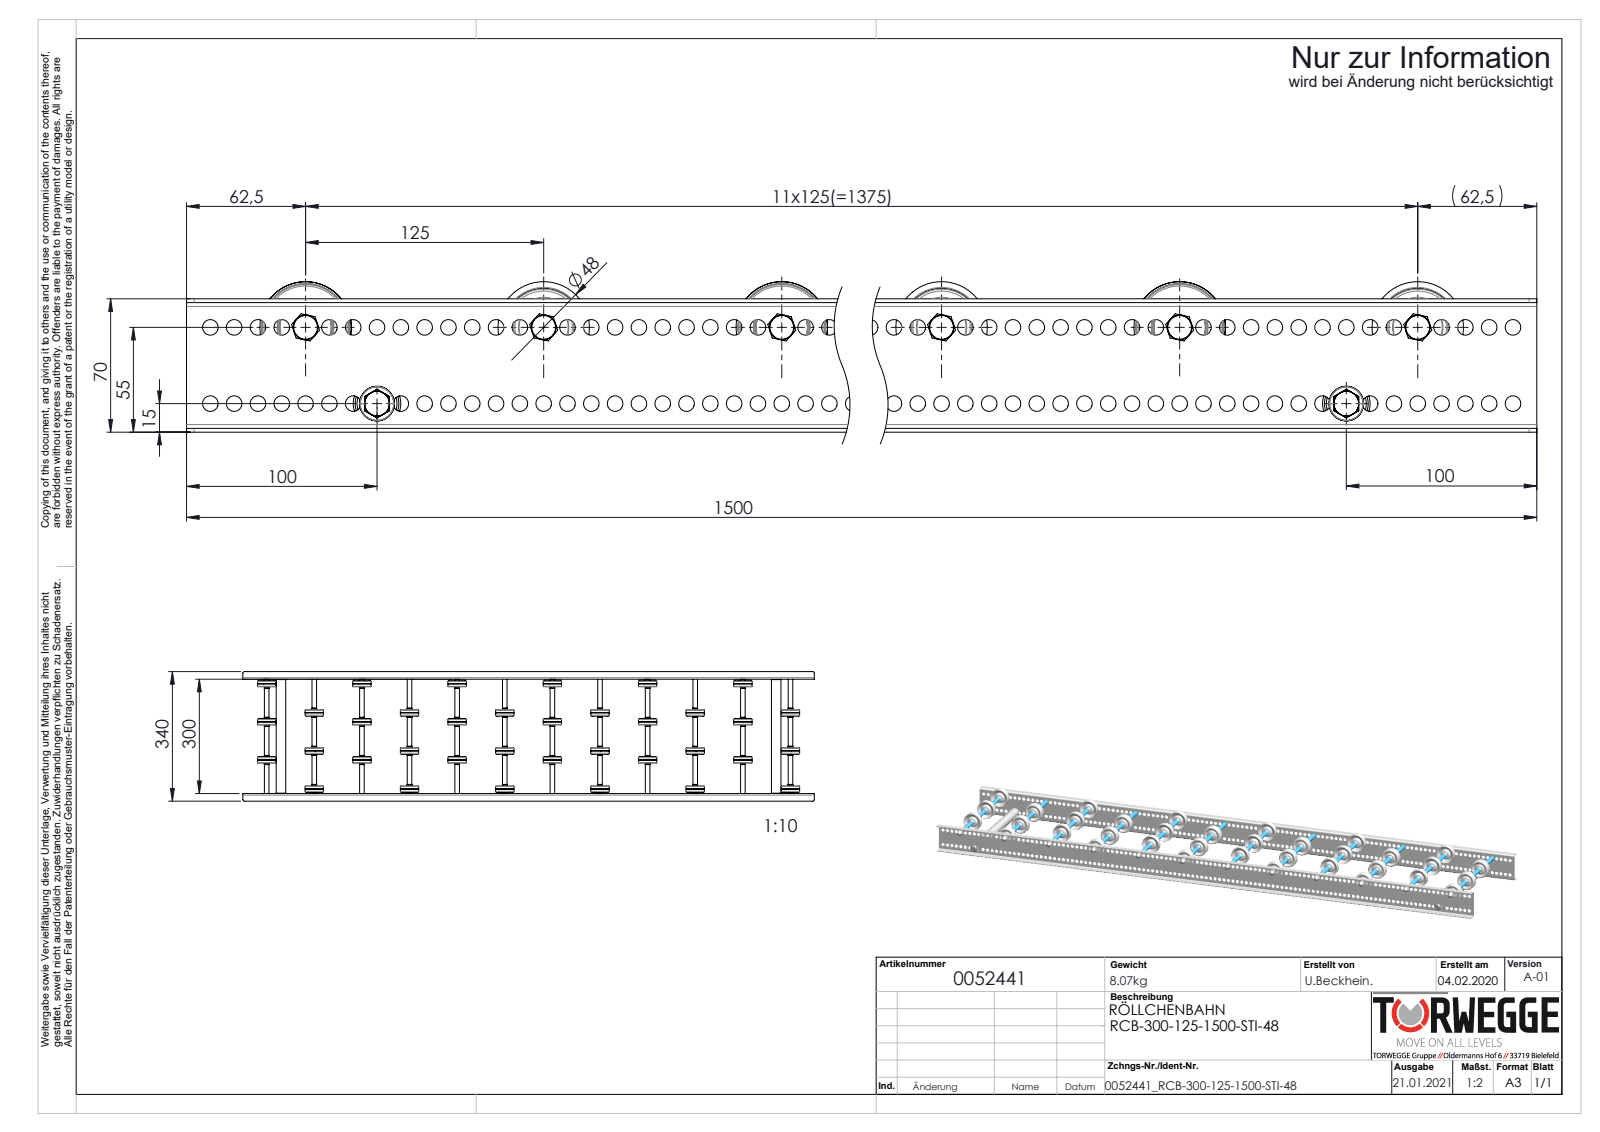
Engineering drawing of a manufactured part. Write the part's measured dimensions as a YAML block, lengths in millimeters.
part_name: "0052441; S106837_Gewindestange-M8-KFG_L320; Traversen_KFG_L300; 0046278_KB-ROHR-12X1,75mm_KFG_L76 (+5 more)"
step_written_by: "SolidWorks 2020 (AUTOMOTIVE_DESIGN)"
units: millimeters
bodies: {solids: 156, faces: 5096, planar: 984, cylindrical: 2208, other: 1904}
overall_size: [1500, 340, 79]
volume: 1769000
surface_area: 1457000
round_holes:
  - {diameter: 8.2, count: 238}
  - {diameter: 6.65, count: 12}
  - {diameter: 8, count: 12}
  - {diameter: 9.65, count: 12}
  - {diameter: 15, count: 12}
  - {diameter: 41, count: 12}
  - {diameter: 6.8, count: 2}
  - {diameter: 21, count: 2}
round_bosses_or_shafts:
  - {diameter: 48, count: 12}
  - {diameter: 13, count: 12}
  - {diameter: 12.5, count: 12}
  - {diameter: 12.4, count: 12}
  - {diameter: 12, count: 12}
  - {diameter: 11.5, count: 12}
  - {diameter: 25, count: 2}
  - {diameter: 8, count: 2}
partial_cylinders:
  - {radius: 4, count: 8}
  - {radius: 2, count: 4}
face_to_face_distances: [2, 302, 68, 100, 304, 300, 76, 70, 66, 12]
hole_center_spacings: [12.5, 25, 37.5, 50, 62.5, 75, 87.5, 100]
